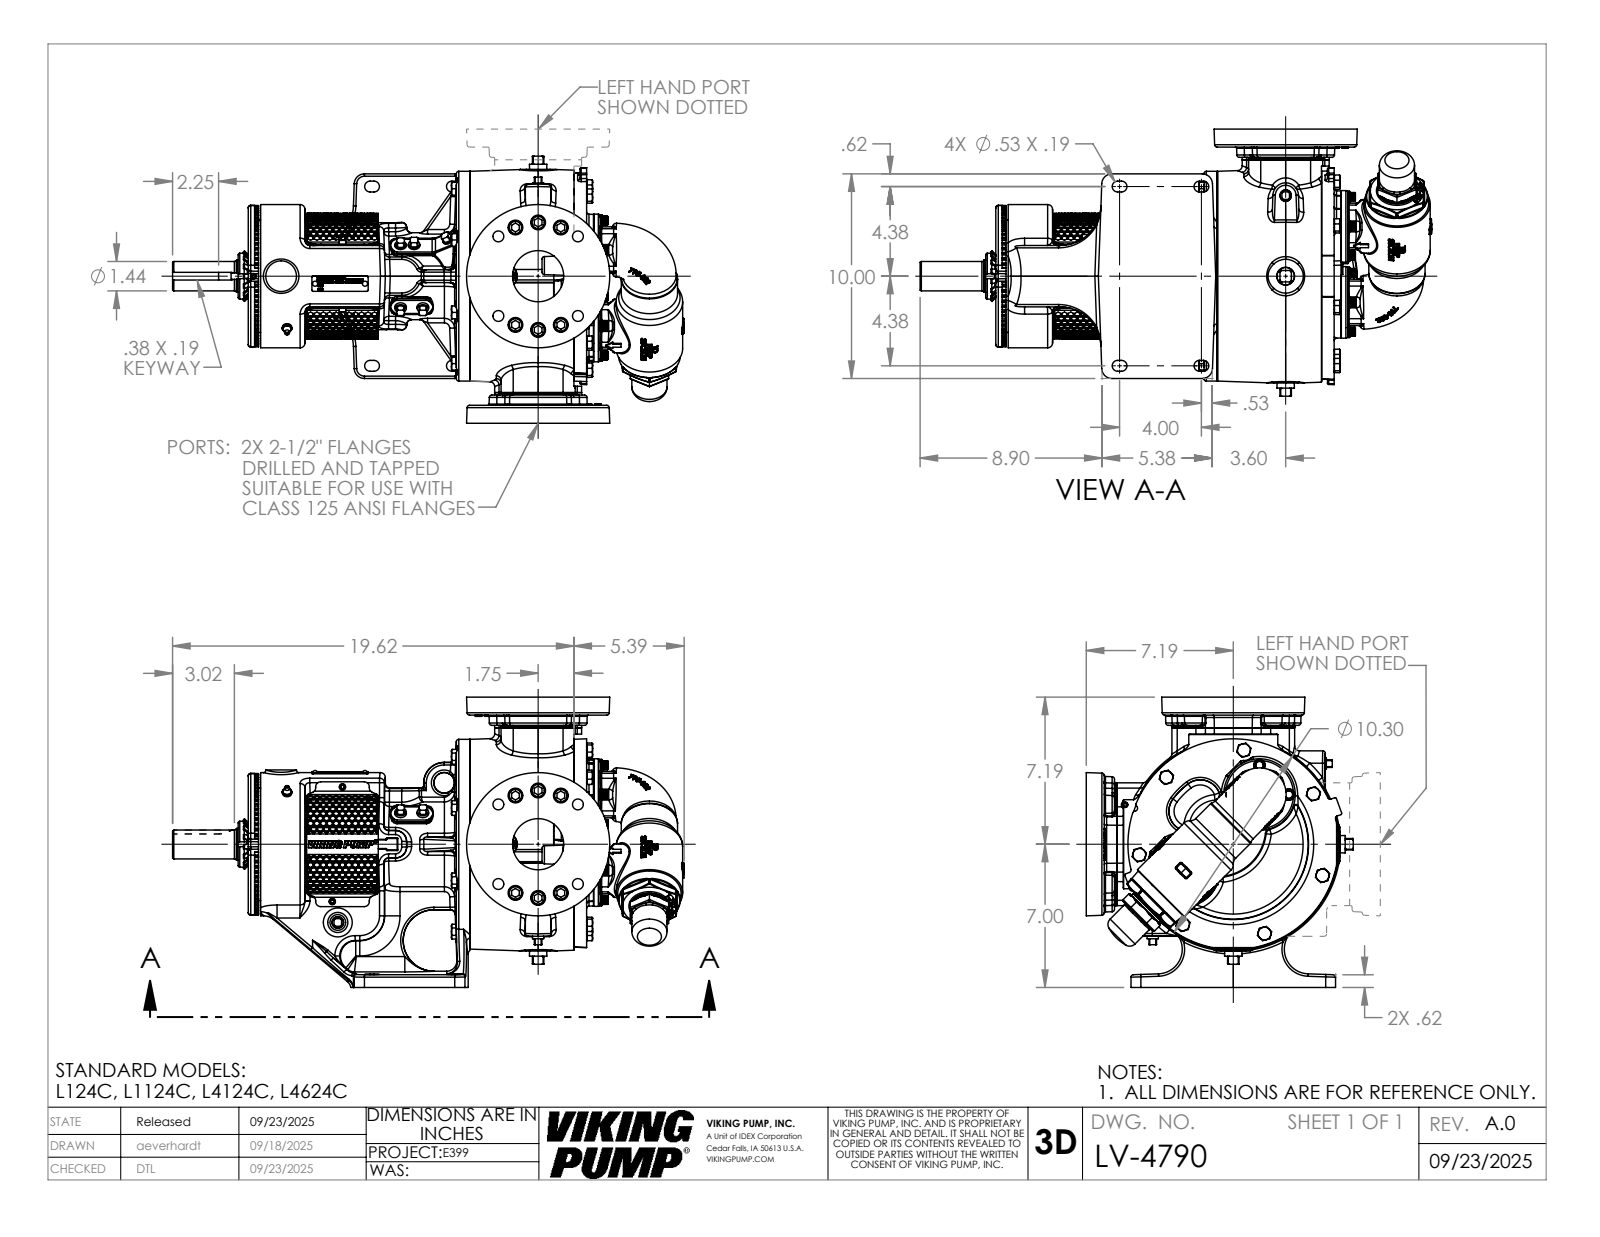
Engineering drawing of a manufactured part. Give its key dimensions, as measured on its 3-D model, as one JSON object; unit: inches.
{"part_name": "LV-4790", "step_written_by": "SolidWorks 2024 (AUTOMOTIVE_DESIGN)", "units": "inches", "bodies": {"solids": 1, "faces": 5694, "planar": 1860, "cylindrical": 1193, "other": 2641}, "overall_size": [25.01, 14.188, 13.053], "volume_in3": 986.7, "surface_area_in2": 1455, "round_holes": [[0.719, 12], [0.406, 8], [0.41, 8], [0.531, 8], [1.094, 8], [0.199, 6], [0.25, 6], [0.159, 3], [0.266, 2], [0.313, 2], [2.5, 2], [0.453, 1]], "round_bosses_or_shafts": [[0.66, 12], [0.625, 9], [0.563, 8], [0.625, 6], [0.375, 4], [0.375, 4], [3.5, 3], [0.437, 3]], "partial_cylinders_radius": [[0.063, 109], [0.12, 76], [0.069, 74], [0.24, 48], [0.03, 36], [0.06, 16], [0.45, 16], [1, 16]], "face_to_face_distances": [14.187, 0.5, 13.792, 3.537, 10.255, 0.88, 0.62, 2.25, 2.143, 5.68], "hole_center_spacings": [3, 2.75, 2.625, 1.375, 3.085, 0.941, 1.136, 2.06]}
